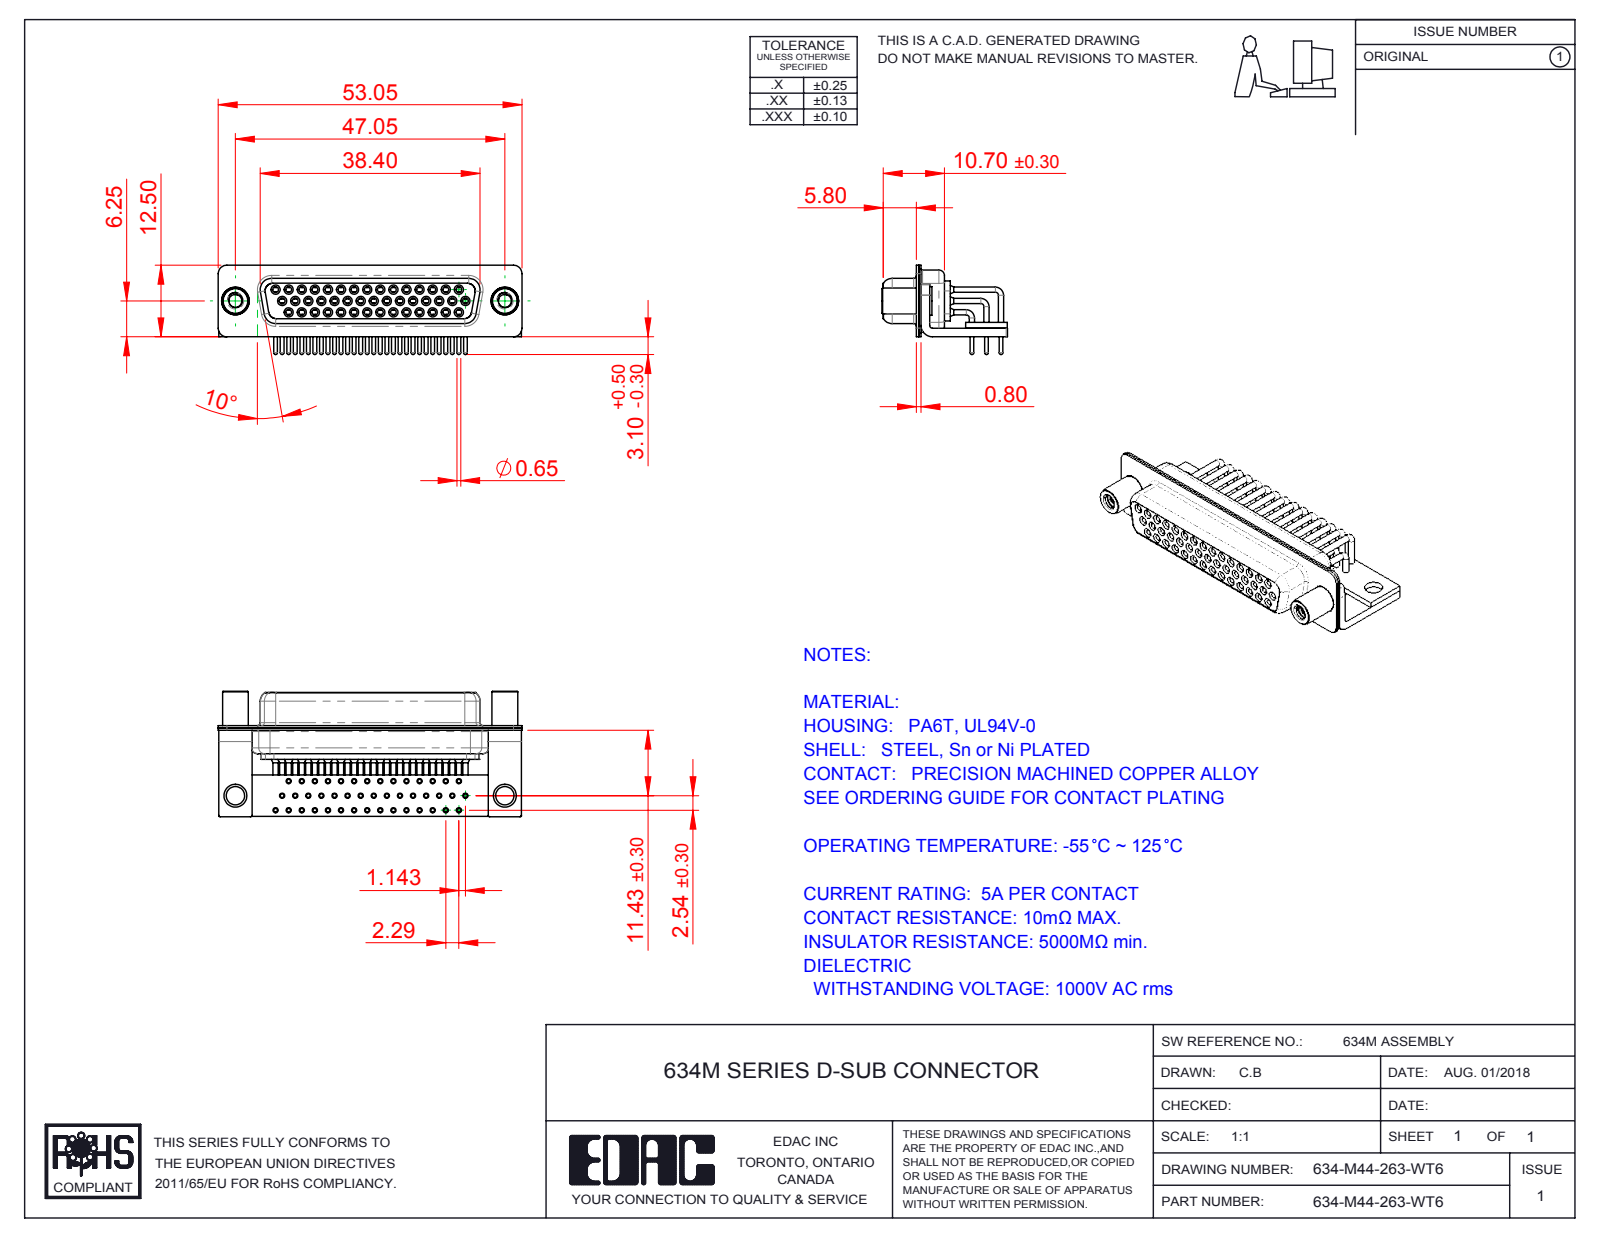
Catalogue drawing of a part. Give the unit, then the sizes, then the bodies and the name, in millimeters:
Units: millimetres
Overall size (bounding box): 53.05 × 21.9 × 15.6
Round holes (diameter × count): ⌀0.9 ×44, ⌀1 ×44, ⌀1.1 ×44, ⌀1.7 ×44, ⌀1.8 ×44, ⌀2 ×44, ⌀2.26 ×2, ⌀3.2 ×2, ⌀4 ×2, ⌀4.8 ×2
Round bosses / shafts (diameter × count): ⌀1.6 ×44, ⌀1.5 ×44, ⌀0.9 ×44, ⌀0.65 ×44, ⌀5 ×2, ⌀4.9 ×2, ⌀4.5 ×2
Partial cylindrical surfaces — rounded edges, fillets, slot ends (radius × count): R0.25 ×16, R1.5 ×16, R2 ×13, R1.35 ×8, R1.6 ×8, R0.5 ×5, R0.6 ×4, R0.65 ×4
Main face-to-face distances: 0.4, 2.3, 1.9, 1, 0.8, 8.5, 9.35, 1.45, 8.95, 1.5
Hole centre spacings: 2.28, 2.29, 4.57, 6.86, 11.43, 3.96, 8.24, 9.14
Volume: 4 584 mm³ · Surface area: 14 913 mm²
Bodies: 52 solids, 2799 faces (755 planar, 1301 cylindrical, 743 other)
Part name (STEP PRODUCT): 634M Shell Front_44 Contacts; 634-M44-263-WT6; 634M Shell Rear_44 Contacts; 634M Contact Row 1 (+6 more)
STEP written by: SolidWorks 2016 (CONFIG_CONTROL_DESIGN)
